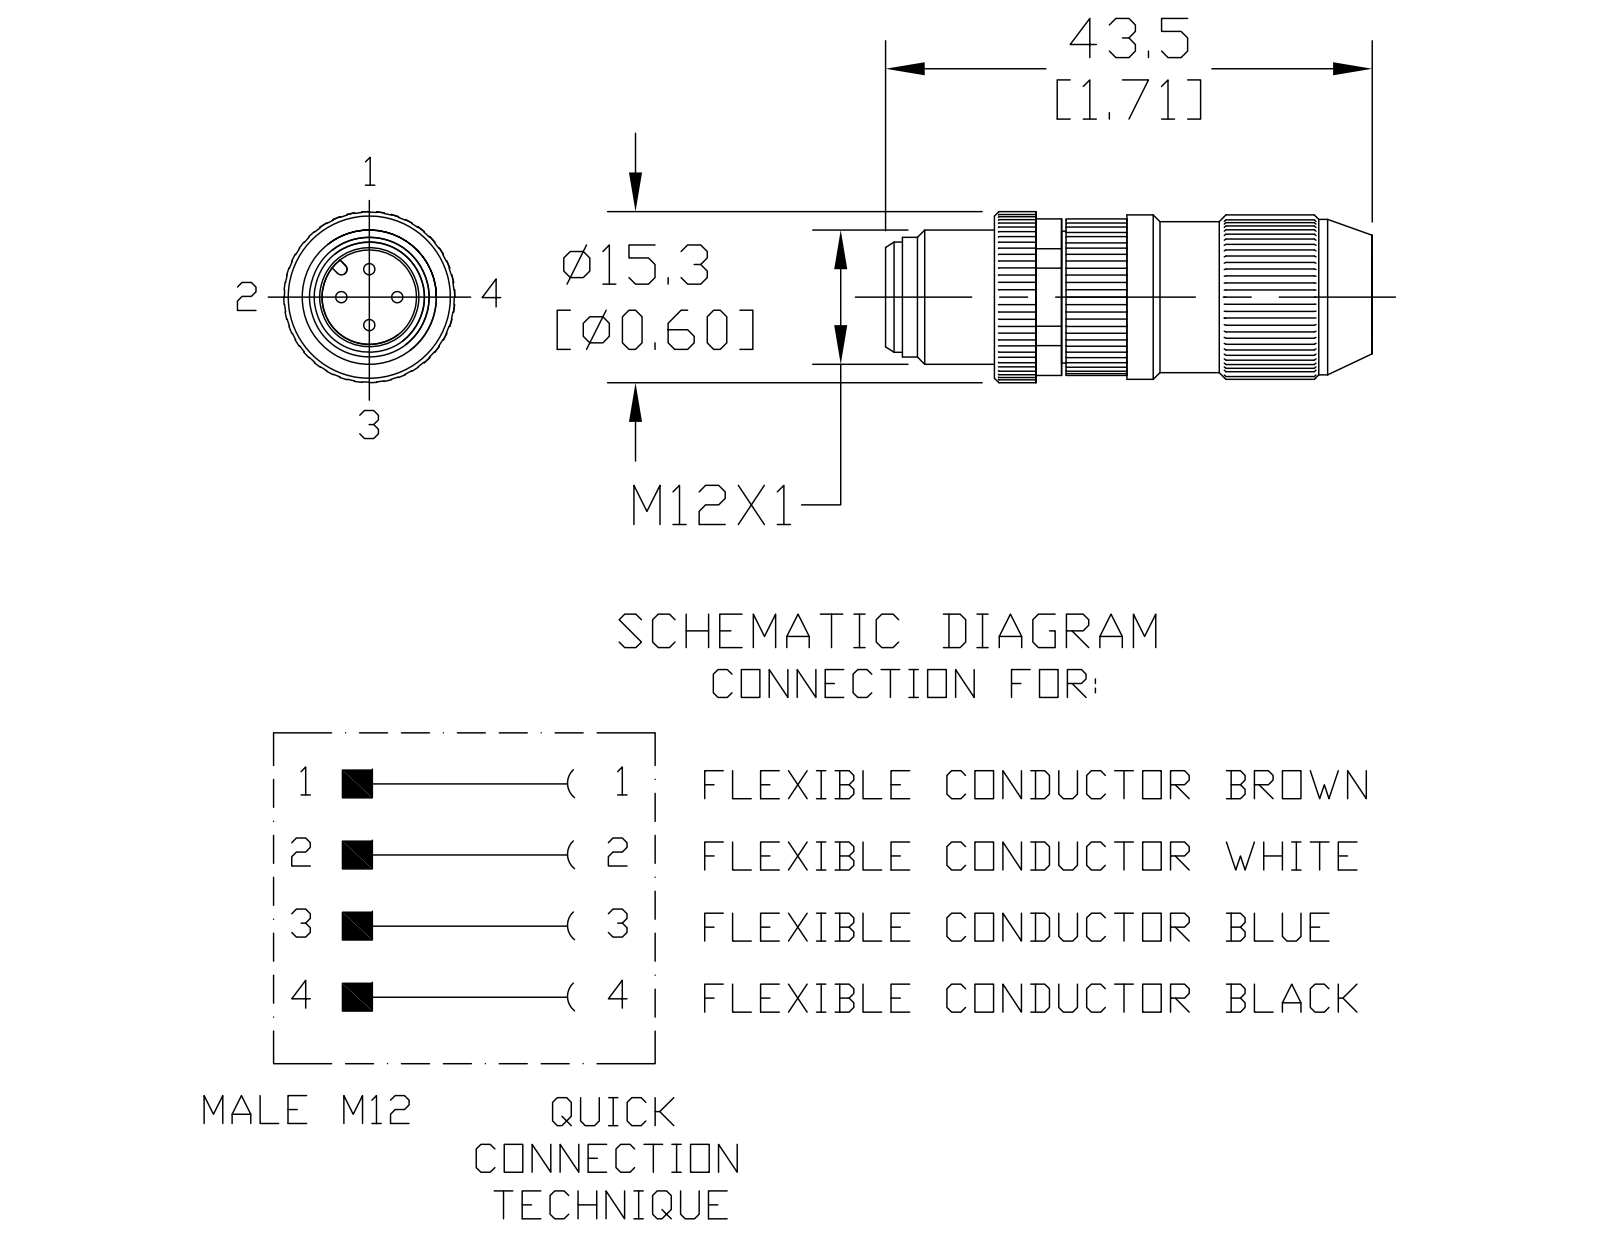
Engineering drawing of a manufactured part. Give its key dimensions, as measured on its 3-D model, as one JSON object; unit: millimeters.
{"part_name": "7000-12491-0000000", "step_written_by": "SolidWorks 2017 (AUTOMOTIVE_DESIGN)", "units": "millimeters", "bodies": {"solids": 1, "faces": 502, "planar": 227, "cylindrical": 235, "other": 40}, "overall_size": [46.75, 15.3, 15.3], "volume_mm3": 6073, "surface_area_mm2": 3027, "round_holes": [[5.2, 1], [6.1, 1], [8.45, 1]], "round_bosses_or_shafts": [[1, 4], [14.7, 1], [13.9, 1], [13.5, 1], [12, 1], [11.8, 1], [10.7, 1], [9.85, 1]], "partial_cylinders_radius": [[0.5, 1], [7, 1], [7.2, 1], [7.55, 1], [7.6, 1], [7.65, 1]], "face_to_face_distances": [29.75, 6.4, 36.15, 1.8, 8.2, 37.95, 5.5, 3.7, 2.7, 32.45]}
